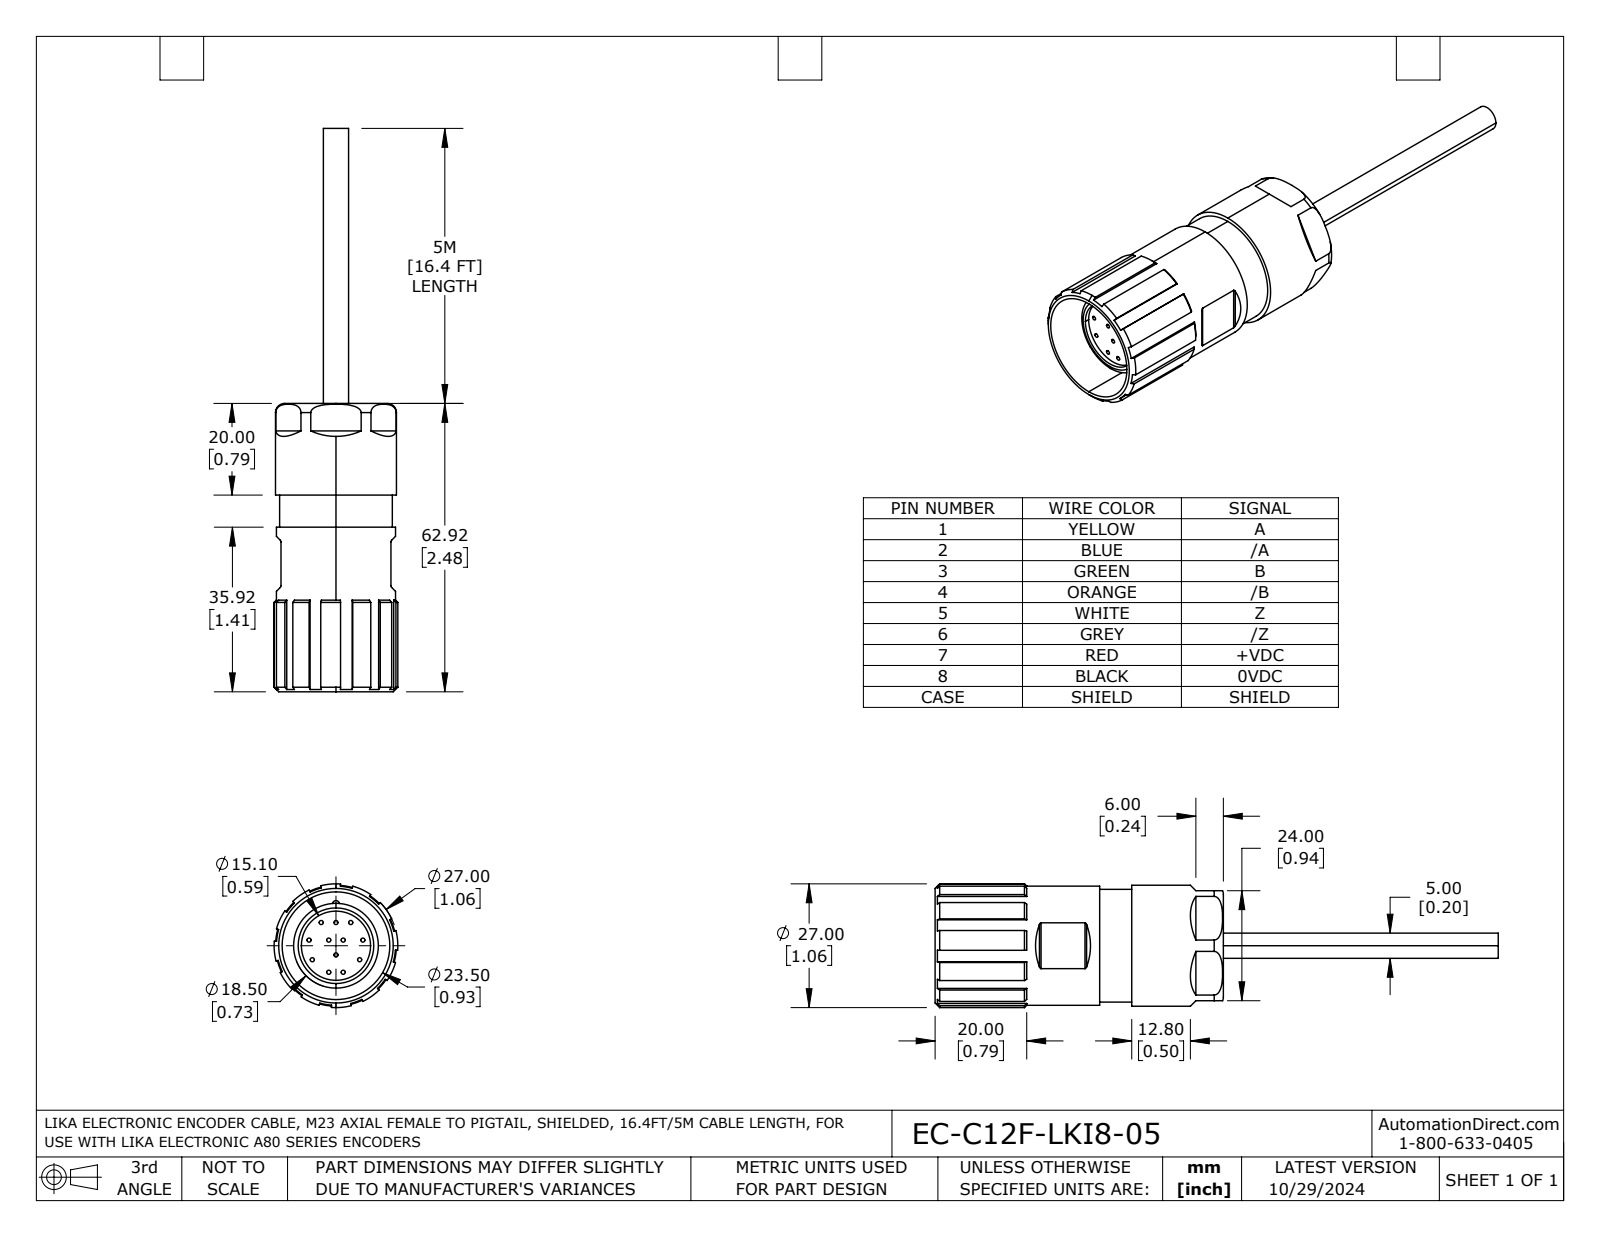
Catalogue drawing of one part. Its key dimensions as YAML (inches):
part_name: "EC-C12F-LKI8-05"
step_written_by: "SolidWorks 2021 (AUTOMOTIVE_DESIGN)"
units: inches
bodies: {solids: 1, faces: 146, planar: 64, cylindrical: 63, other: 19}
overall_size: [4.839, 1.063, 1.063]
volume: 1.77
surface_area: 15.74
round_holes:
  - {diameter: 0.035, count: 12}
  - {diameter: 0.594, count: 1}
  - {diameter: 0.677, count: 1}
  - {diameter: 0.925, count: 1}
round_bosses_or_shafts:
  - {diameter: 1.039, count: 1}
  - {diameter: 1.024, count: 1}
  - {diameter: 0.969, count: 1}
  - {diameter: 0.728, count: 1}
  - {diameter: 0.217, count: 1}
partial_cylinders:
  - {radius: 0.02, count: 4}
  - {radius: 0.03, count: 1}
  - {radius: 0.531, count: 1}
face_to_face_distances: [0.945, 1.985, 0.335, 1.65, 2.182, 1.847, 0.197, 0.591, 1.394, 1.06]
hole_center_spacings: [0.236, 0.079, 0.124, 0.127, 0.142, 0.162, 0.163, 0.164]
